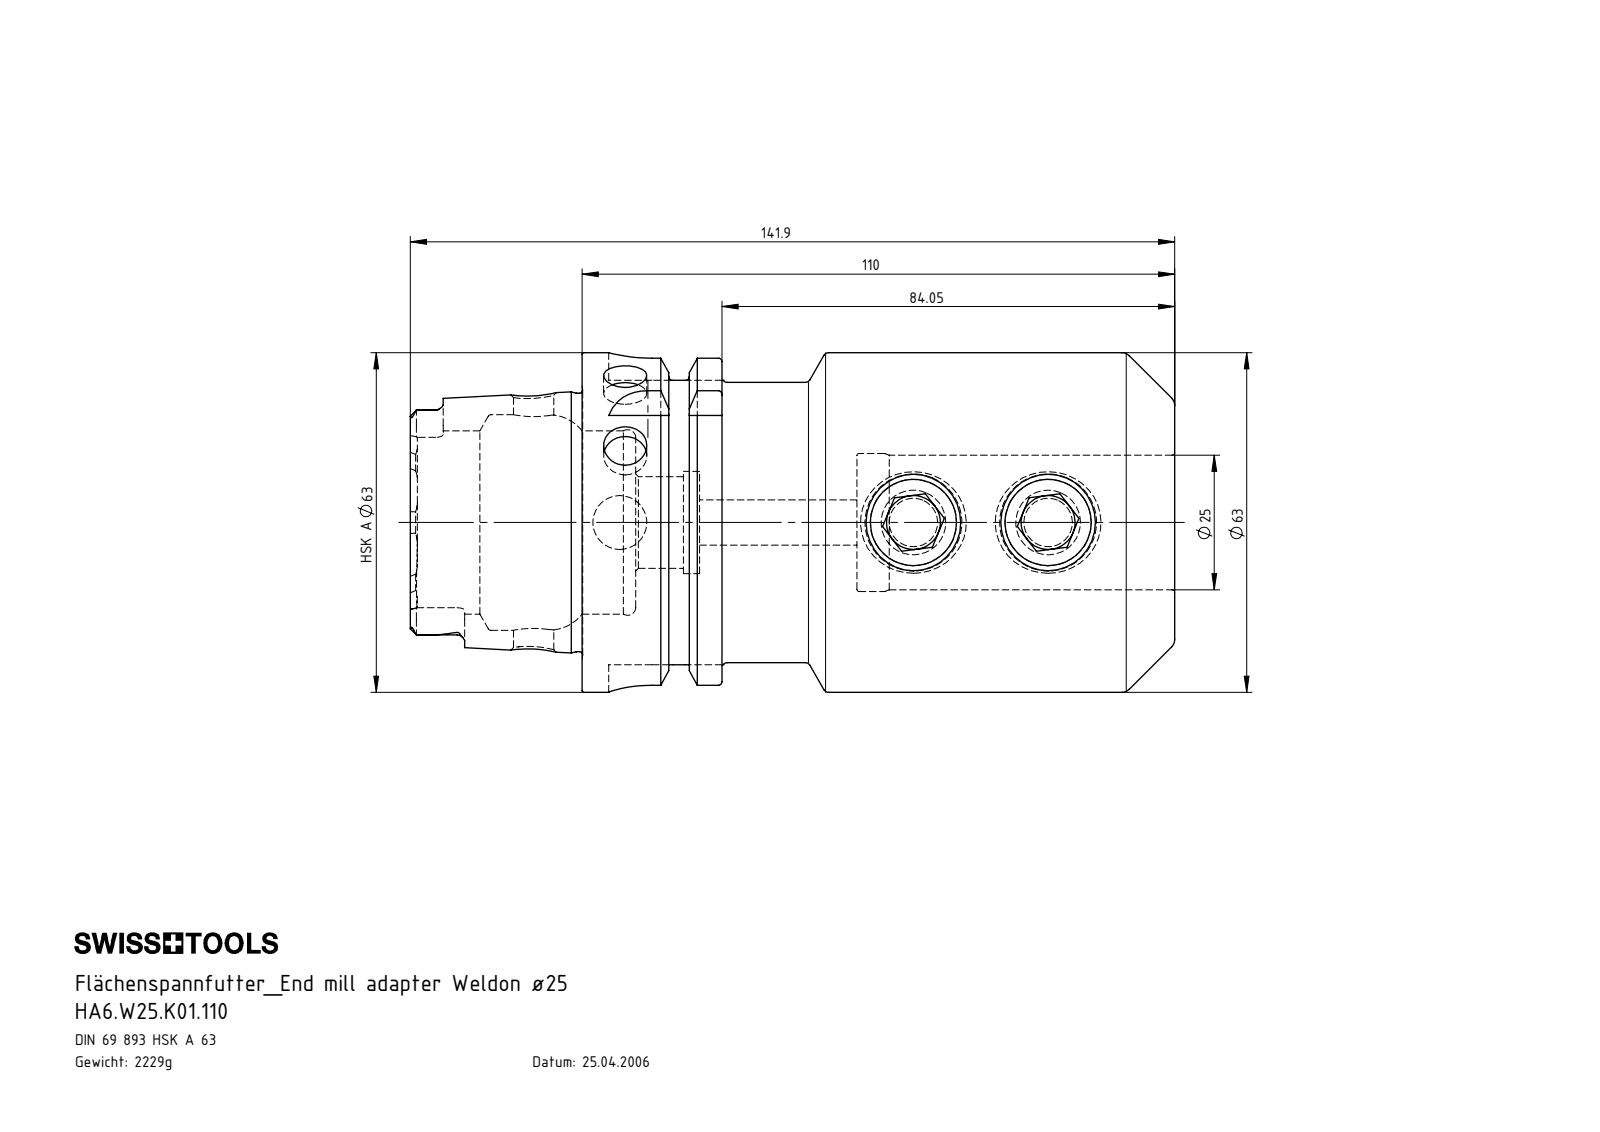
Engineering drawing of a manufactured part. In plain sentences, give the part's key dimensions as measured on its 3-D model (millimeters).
The part is named "HA6.W25.K01.110; W25-ER1.001.020; HA6-W25.K01.110_C_Fertigbearbeitung". Its 3-D file was written by "SolidWorks 2012 (CONFIG_CONTROL_DESIGN)". It is 3 solids with 258 faces: 78 planar, 63 cylindrical and 117 other. Overall it measures 141.9 by 63 by 63 millimeters. Its volume is 283 942 cubic millimeters and its surface area 49 295 square millimeters. Round holes: 2 of diameter 8, 2 of diameter 16, 1 of diameter 7.5, 1 of diameter 8.4, 1 of diameter 10, 1 of diameter 17, 1 of diameter 19, 1 of diameter 25, 1 of diameter 25.6, 1 of diameter 34, 1 of diameter 40. Round bosses or shafts: 2 of diameter 18, 1 of diameter 63, 1 of diameter 54.95, 1 of diameter 52, 1 of diameter 47.94. Partial cylindrical surfaces (rounded edges, fillets, slot ends): 6 of radius 1.4, 4 of radius 2.88, 4 of radius 8. The main face-to-face distances are 110, 25.95, 84.05, 16, 9.95, 100.05, 51, 41.05, 25.05, 59. The hole center spacings are 25, 54.5, 79.5.
